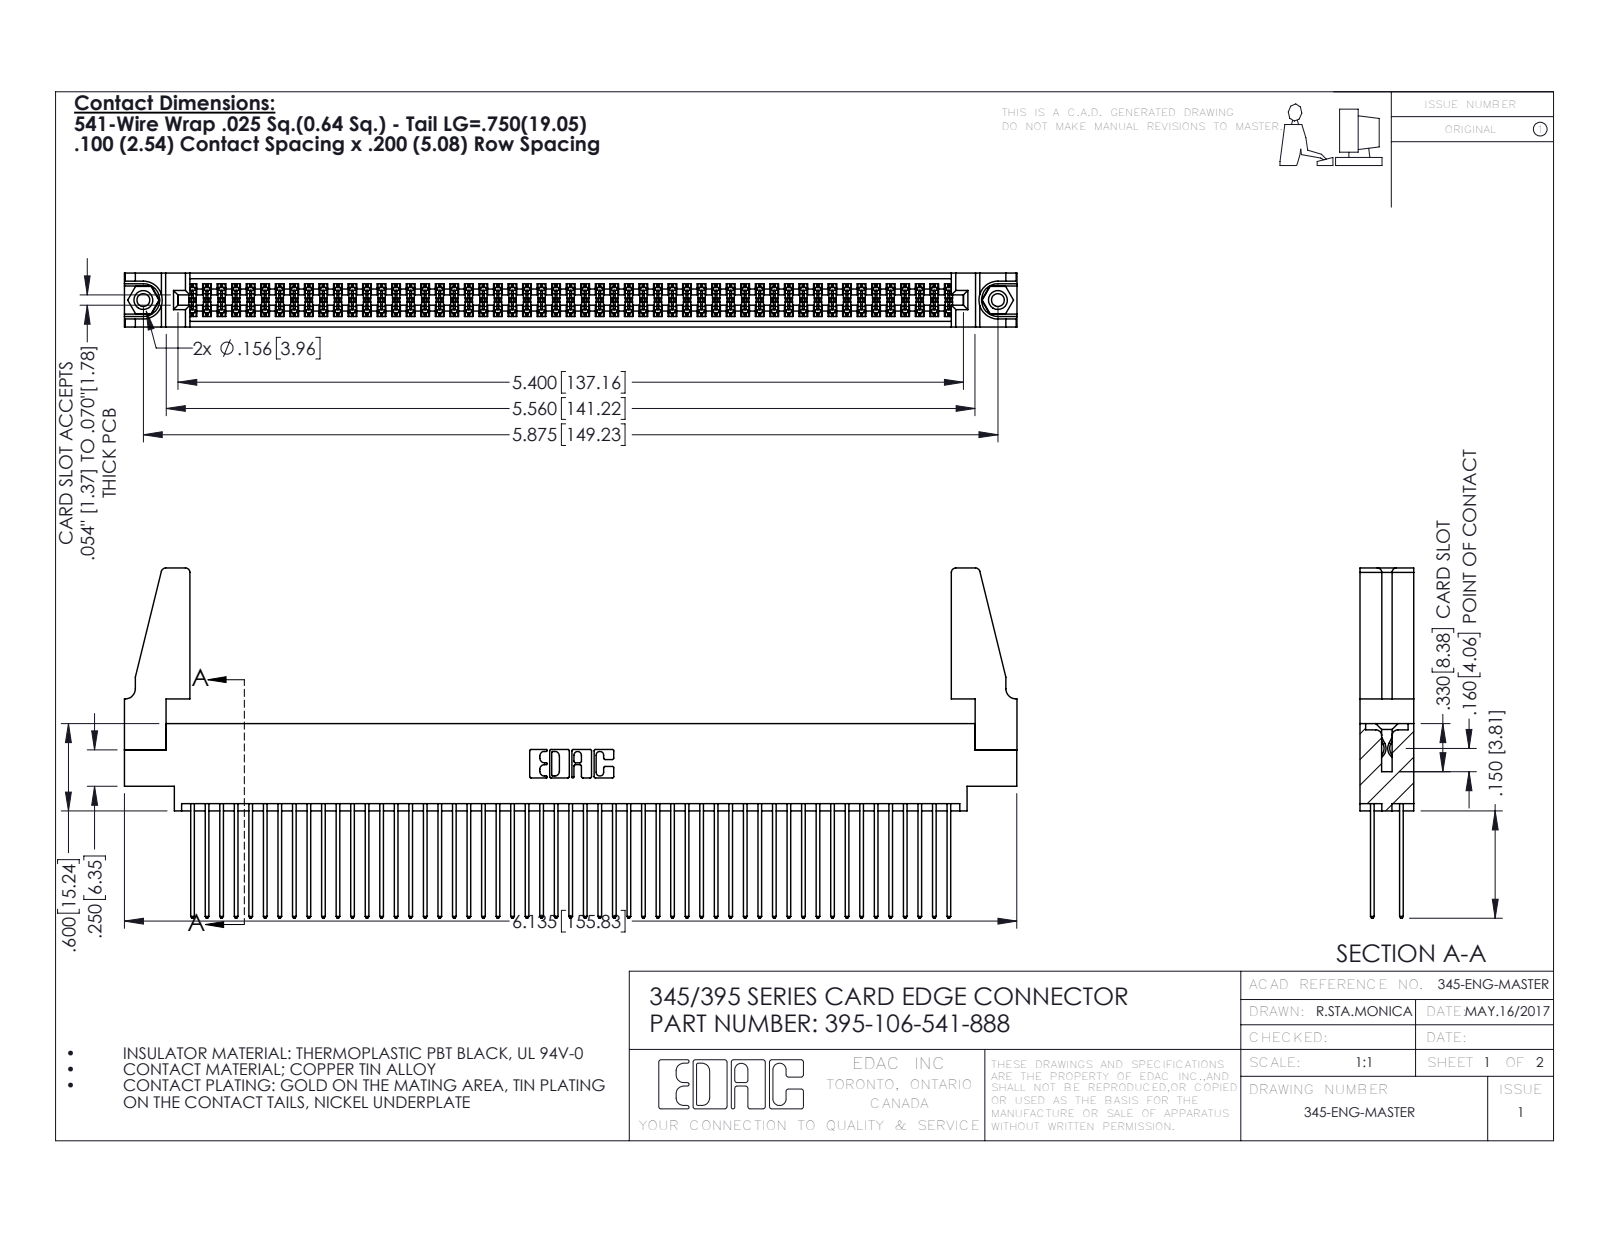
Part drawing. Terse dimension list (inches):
name: 345-220-078_345-220-088; 395-106-541-888; 345-250-001_345-250-001-102; 345 Part_0.170 Offset - 0.156 Dia-TH (+1 more)
written by: SolidWorks 2016 (CONFIG_CONTROL_DESIGN)
unit: in
bodies: 111 solids, 5554 faces (3654 planar, 1884 cylindrical, 16 other)
size: 6.136 × 2.407 × 0.37
volume: 1.159 in³; area: 45.88 in²
holes: 2× ⌀0.089, 2× ⌀0.125, 2× ⌀0.156, 1× ⌀0.064
bosses: 2× ⌀0.155
rounds: 159× R0.006, 106× R0.01, 22× R0.01, 8× R0.03, 6× R0.007, 6× R0.031, 3× R0.026, 2× R0.014
face distances: 0.072, 0.298, 0.2, 0.098, 0.272, 0.025, 0.37, 0.225, 0.175, 0.149
hole spacings: 0.27, 5.639, 5.875
